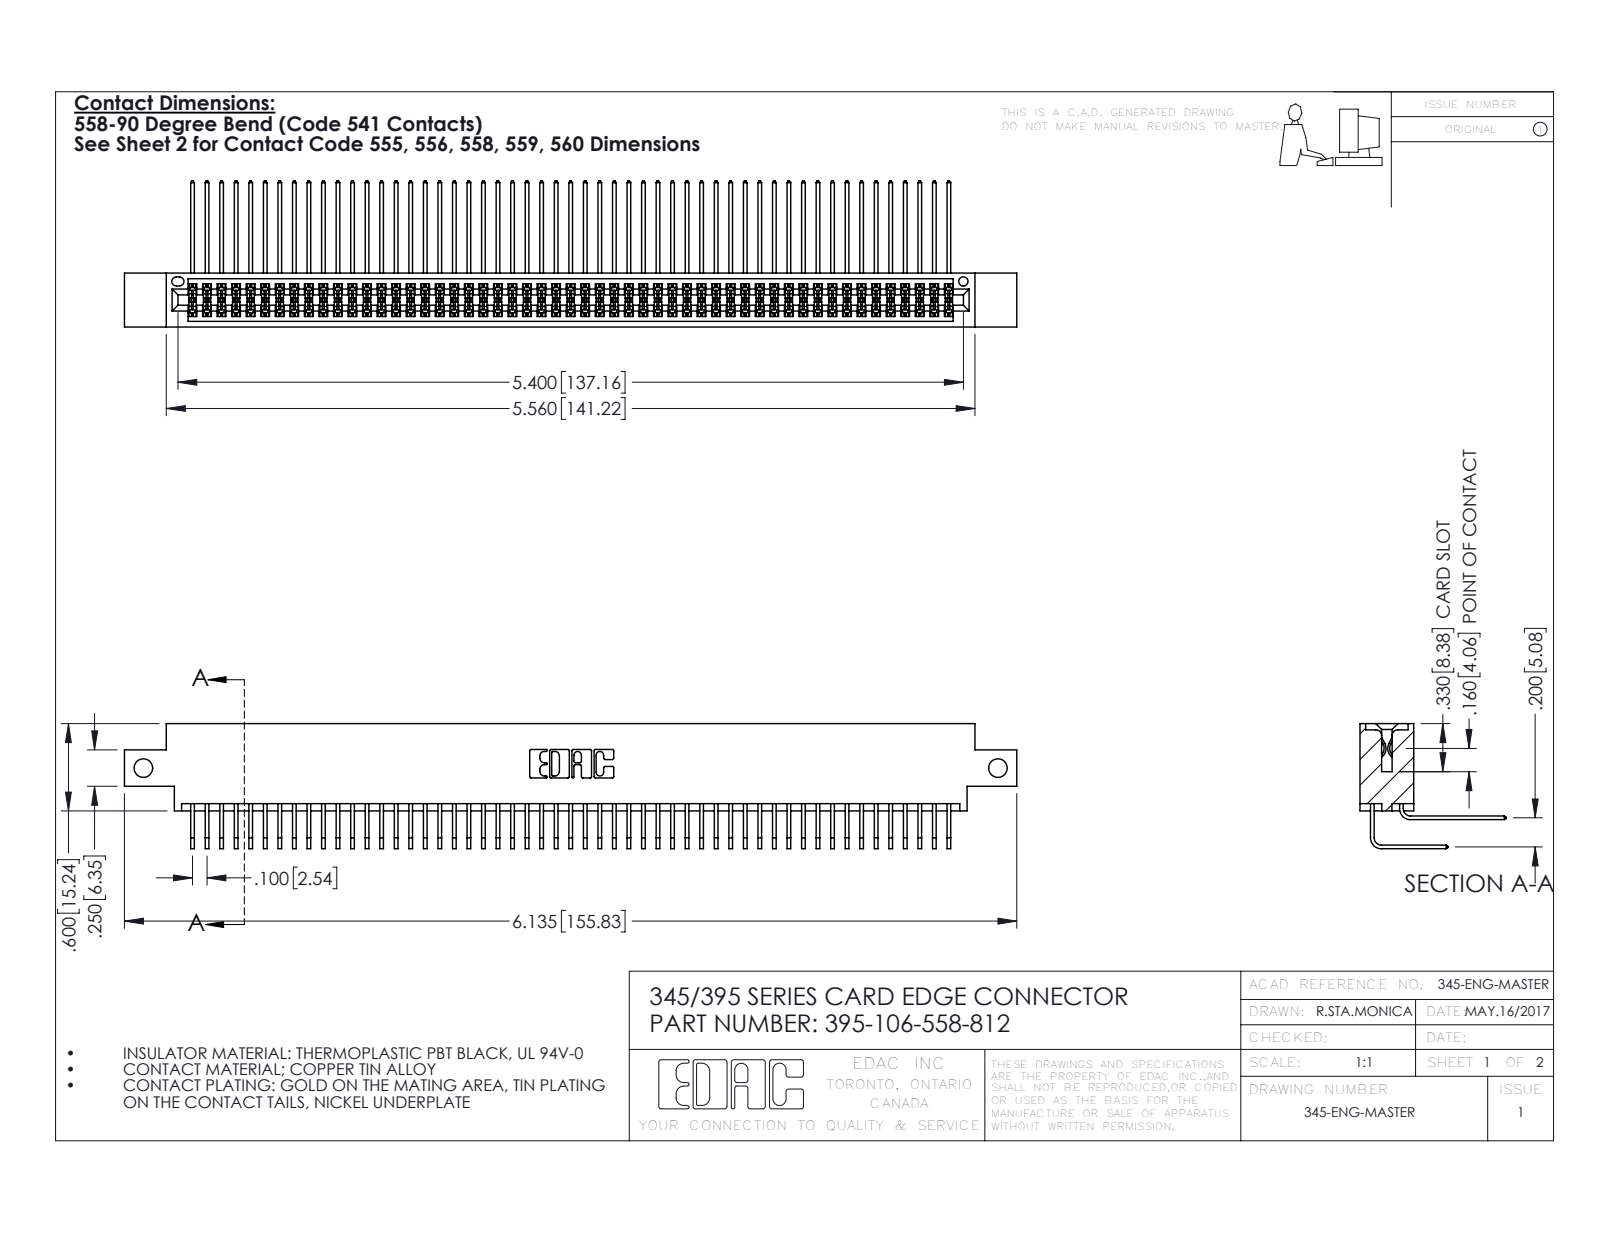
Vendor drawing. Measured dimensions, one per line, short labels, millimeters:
name: 345-292-001_558 559 Tail - 1; 345-292-001_558 Tail - 2; 395-106-558-812; 345 Part_0.170 Offset - Side Mount
written by: SolidWorks 2016 (CONFIG_CONTROL_DESIGN)
unit: mm
bodies: 107 solids, 5642 faces (3794 planar, 1848 cylindrical, 0 other)
size: 155.8 × 25.5 × 21.8
volume: 15 600 mm³; area: 26 230 mm²
holes: 2× ⌀3.3, 1× ⌀1.6
rounds: 160× R0.2, 22× R0.3, 6× R0.2, 6× R0.8, 3× R0.7, 2× R0.4, 2× R0.5, 2× R0.6
face distances: 1.8, 7.6, 5.1, 9.4, 2.5, 6.9, 0.6, 5.7, 4.4, 0.6
hole spacings: 149.2
